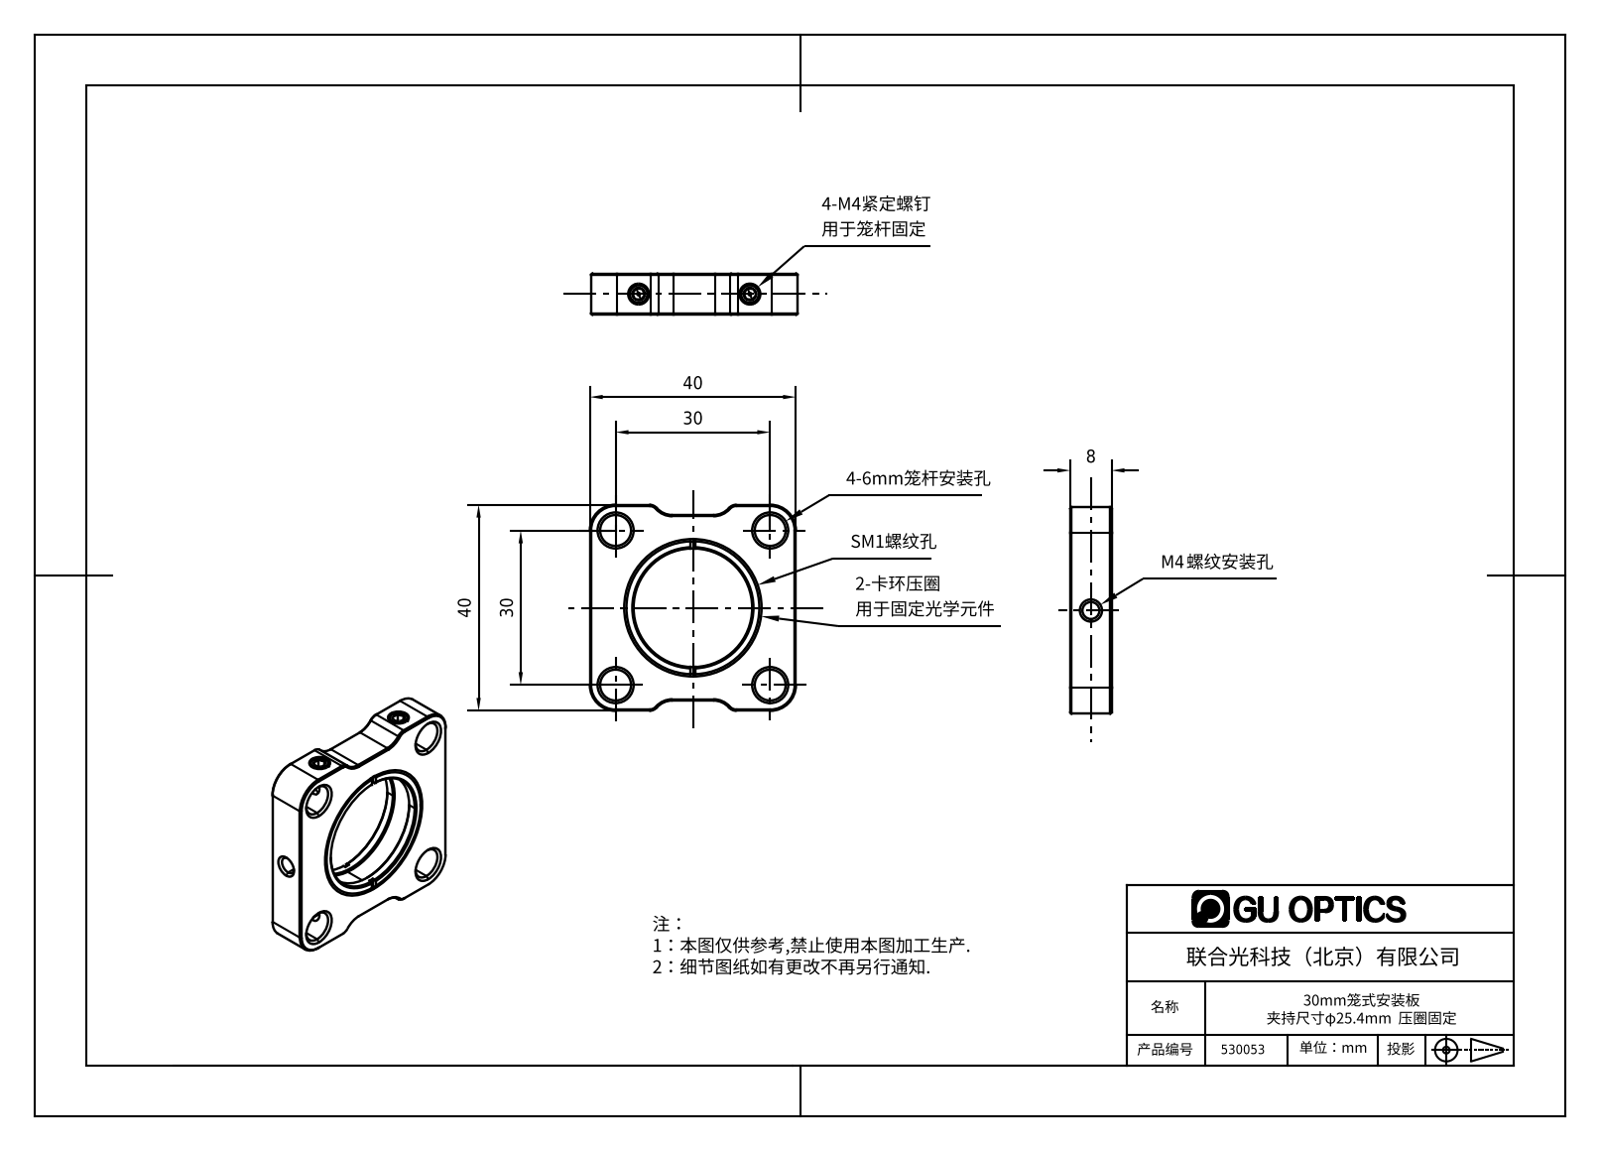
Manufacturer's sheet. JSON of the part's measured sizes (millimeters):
{"part_name": "2.2.1.11_L30B-SM1_30 mm笼板，用于1.0英寸光学元件，附带2个SM1卡环，M4螺纹", "step_written_by": "SolidWorks 2018 (AUTOMOTIVE_DESIGN)", "units": "millimeters", "bodies": {"solids": 0, "faces": 230, "planar": 76, "cylindrical": 36, "other": 118}, "overall_size": [40, 40, 8], "round_holes": [[6, 4], [3.3, 3], [23.01, 1], [25.65, 1]], "partial_cylinders_radius": [[2, 4], [4, 4], [5, 4]], "face_to_face_distances": [8, 2, 40, 6, 38, 4, 36, 33.58, 2.1, 1.41], "hole_center_spacings": [21.21, 30, 42.43, 21.6]}
